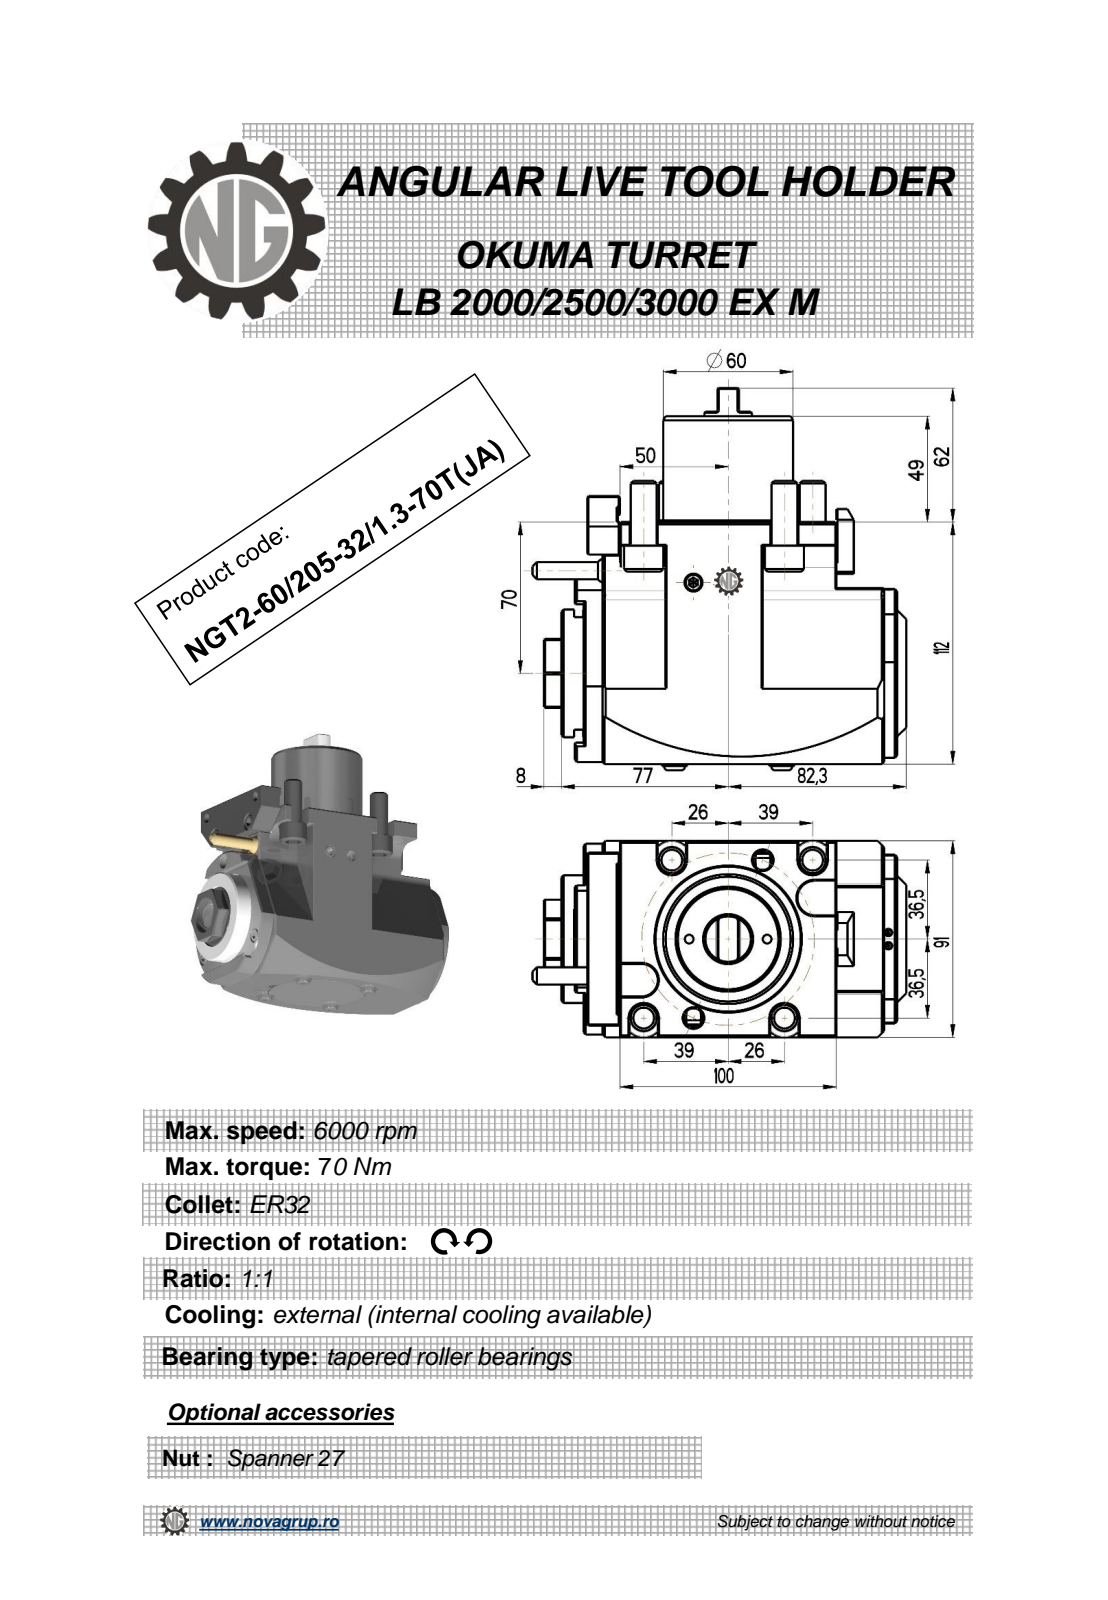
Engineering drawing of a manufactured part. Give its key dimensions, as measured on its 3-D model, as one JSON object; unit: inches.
{"part_name": "NGT2_60_205_32_1_3_70T_JA", "step_written_by": "PRO/ENGINEER BY PARAMETRIC TECHNOLOGY CORPORATION, 2010280 (CONFIG_CONTROL_DESIGN)", "units": "inches", "bodies": {"solids": 1, "faces": 781, "planar": 425, "cylindrical": 196, "other": 160}, "overall_size": [6.959, 6.797, 3.583], "volume_in3": 84.58, "surface_area_in2": 168.6, "round_holes": [[0.197, 3], [0.354, 2], [0.118, 1], [0.374, 1], [0.906, 1], [2.52, 1]], "round_bosses_or_shafts": [[0.709, 4], [0.472, 4], [0.465, 4], [0.374, 4], [0.236, 3], [0.118, 2], [3.071, 1], [2.5, 1]], "partial_cylinders_radius": [[0.014, 24], [0.009, 20], [0.006, 12], [0.012, 10], [0.01, 6], [0.031, 6], [0.138, 4], [0.142, 4]], "face_to_face_distances": [3.583, 1.929, 4.409, 0.472, 3.976, 0.827, 0.512, 6.339, 5.63, 0.402], "hole_center_spacings": [1.569, 1.941, 3.246, 0.757, 1.268, 1.516, 1.986, 2.232]}
